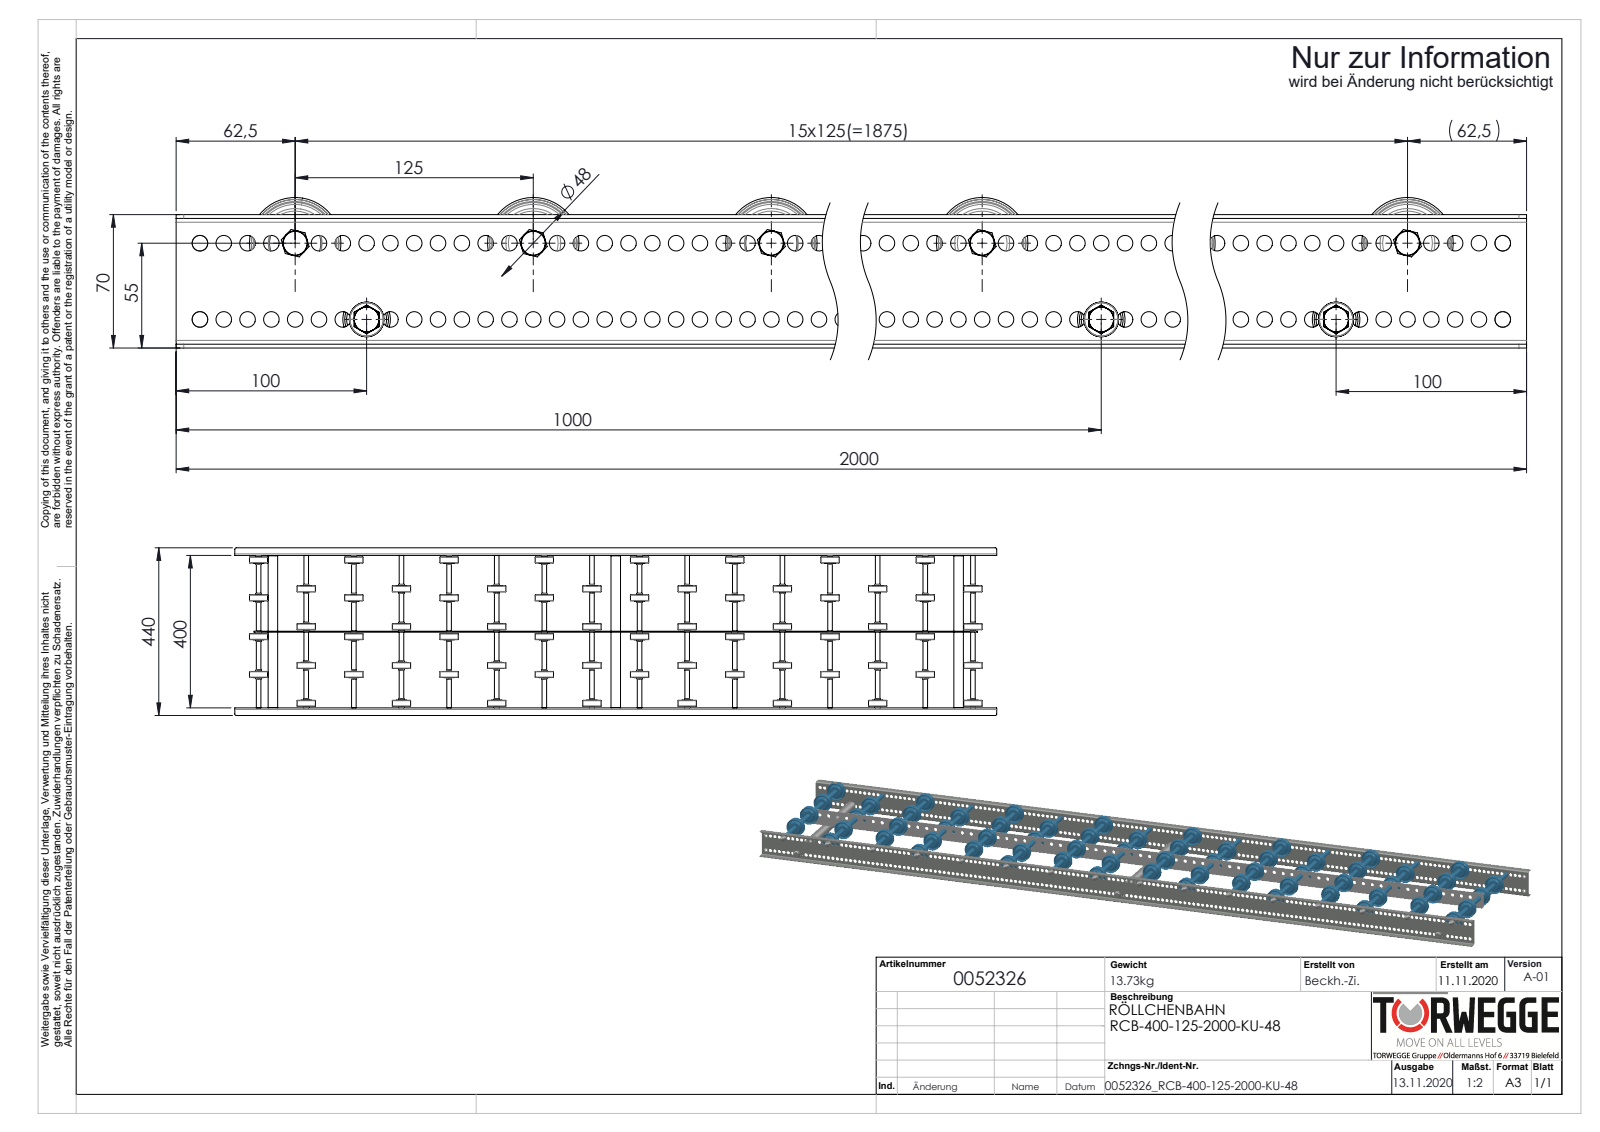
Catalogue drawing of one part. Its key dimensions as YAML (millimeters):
part_name: "Hutmutter_DIN_1587_M8; S106837_Gewindestange-M8-KFG_L420; Traversen_KFG_L400; Röllchenachse-für-Konfiguration_EL400 (+6 more)"
step_written_by: "SolidWorks 2020 (AUTOMOTIVE_DESIGN)"
units: millimeters
bodies: {solids: 194, faces: 7652, planar: 1288, cylindrical: 3072, other: 3292}
overall_size: [2000, 440, 79]
volume: 2945000
surface_area: 2314000
round_holes:
  - {diameter: 8.2, count: 318}
  - {diameter: 8.5, count: 76}
  - {diameter: 6.65, count: 16}
  - {diameter: 9.65, count: 16}
  - {diameter: 13.7, count: 16}
  - {diameter: 6.8, count: 3}
  - {diameter: 21, count: 3}
round_bosses_or_shafts:
  - {diameter: 8, count: 19}
  - {diameter: 48, count: 16}
  - {diameter: 27, count: 16}
  - {diameter: 12.7, count: 16}
  - {diameter: 12.5, count: 16}
  - {diameter: 12, count: 16}
  - {diameter: 25, count: 3}
partial_cylinders:
  - {radius: 4, count: 8}
  - {radius: 2, count: 4}
  - {radius: 5, count: 4}
face_to_face_distances: [2, 402, 68, 404, 400, 201.1, 198.6, 200.9, 198.9, 203.1]
hole_center_spacings: [12.5, 25, 37.5, 50, 62.5, 75, 87.5, 100]
